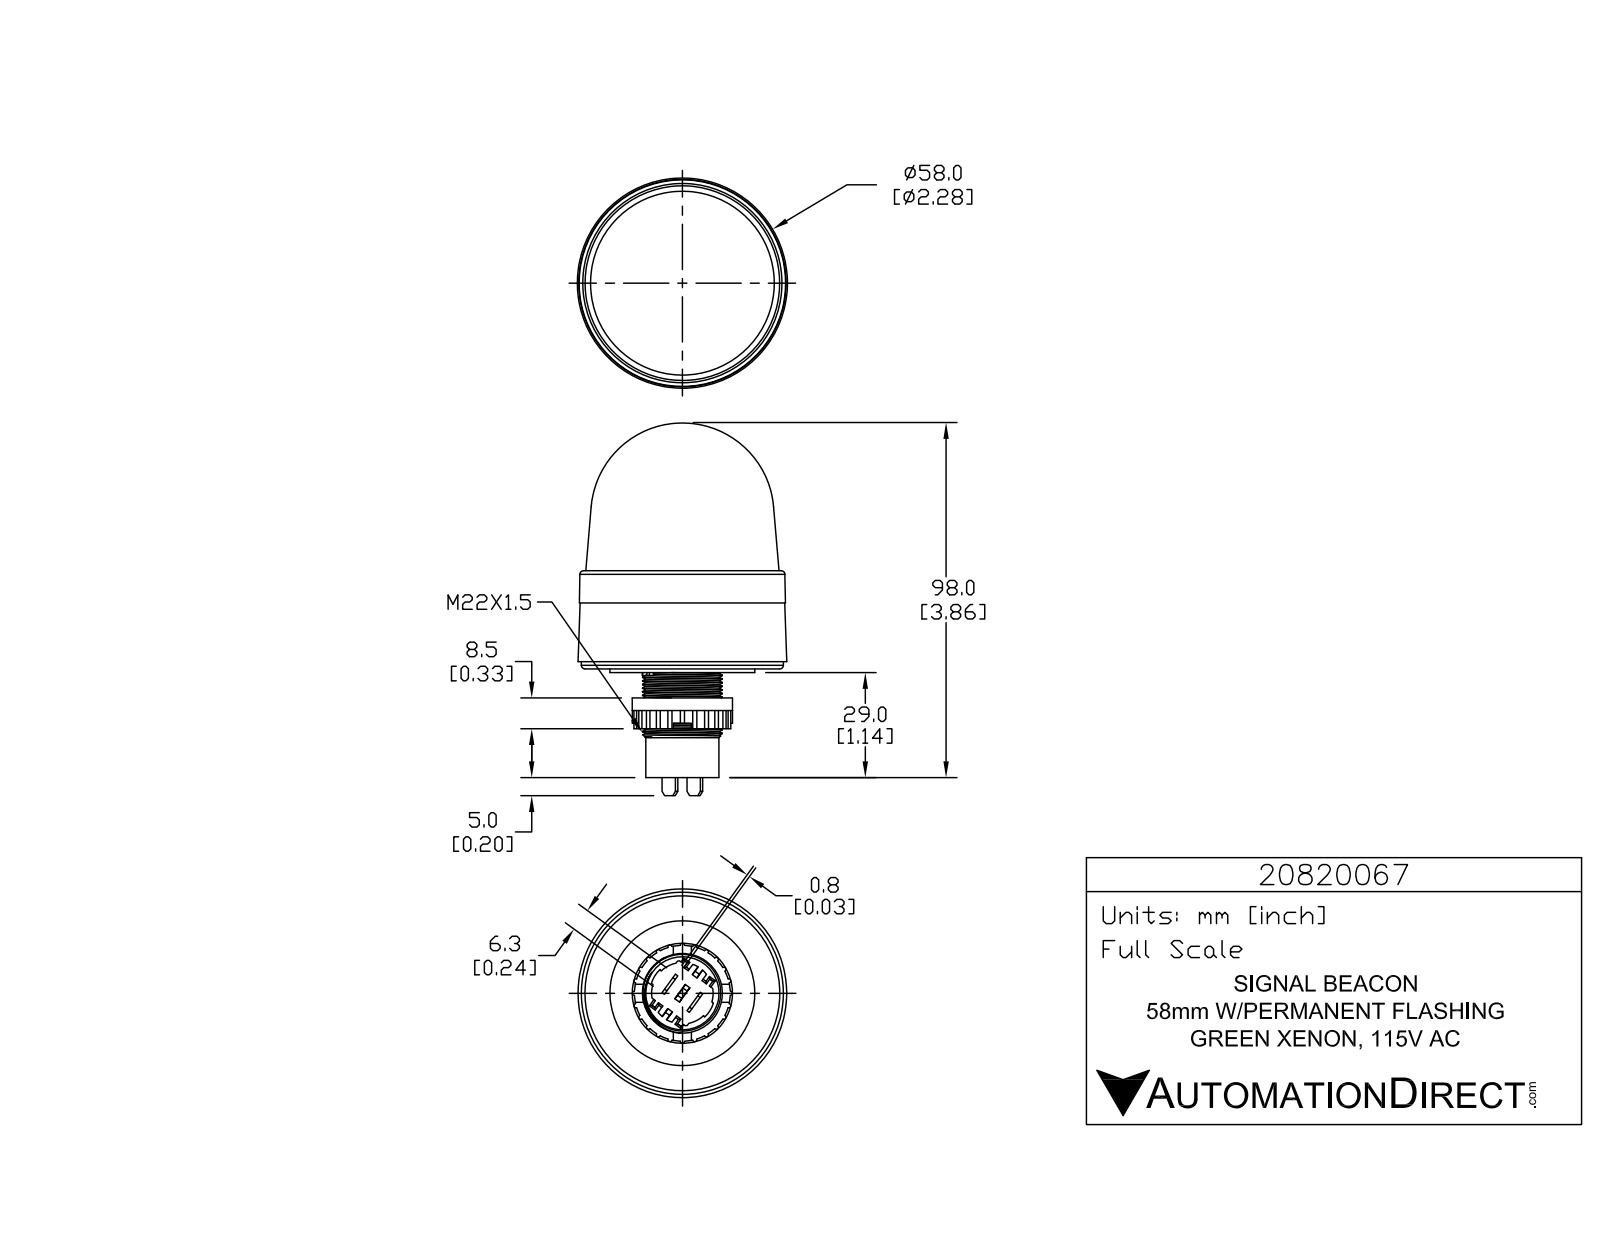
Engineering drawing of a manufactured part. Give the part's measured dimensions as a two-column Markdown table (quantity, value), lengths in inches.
| quantity | value |
| --- | --- |
| part name | 20820067 |
| STEP written by | SolidWorks 2015 (AUTOMOTIVE_DESIGN) |
| units | inches |
| bodies | 1 solid, 266 faces (119 planar, 120 cylindrical, 27 other) |
| overall size | 4.051 × 2.269 × 2.269 |
| volume | 9.016 in³ |
| surface area | 31.05 in² |
| round holes (diameter × count) | 0.906 × 1 |
| round bosses / shafts (diameter × count) | 2.197 × 1, 1.575 × 1, 1.091 × 1, 0.866 × 1, 0.795 × 1 |
| partial cylindrical surfaces (radius × count) | 0.023 × 24, 0.02 × 2, 0.335 × 1, 0.354 × 1, 0.522 × 1 |
| main face-to-face distances | 0.039, 0.276, 0.118, 1.142, 0.335, 0.315, 1.063, 0.748, 1.024, 0.728 |
